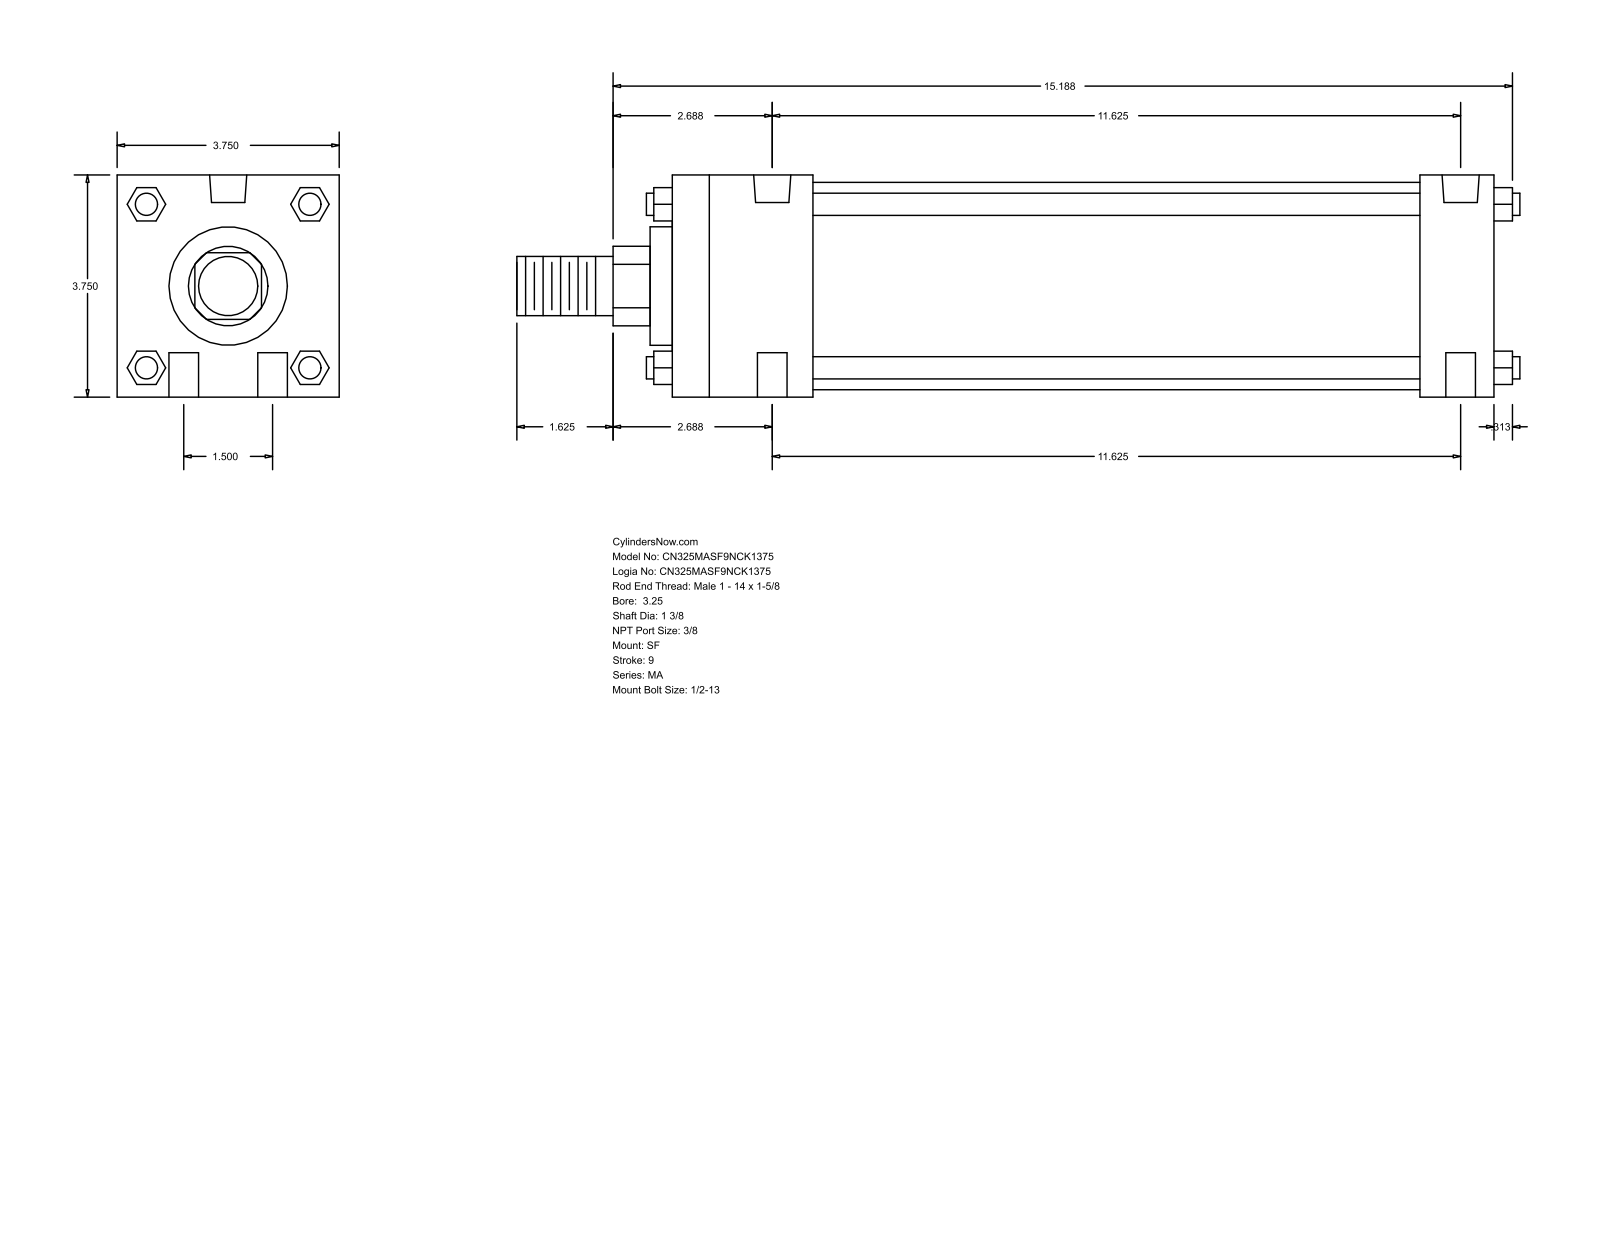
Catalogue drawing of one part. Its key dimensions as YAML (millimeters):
part_name: "MA_SF__0325_1.375"
step_written_by: "GSSL Pune (CONFIG_CONTROL_DESIGN)"
units: millimeters
bodies: {solids: 0, faces: 124, planar: 94, cylindrical: 30, other: 0}
overall_size: [430.21, 95.25, 95.25]
round_holes:
  - {diameter: 12.7, count: 4}
  - {diameter: 11.11, count: 2}
  - {diameter: 15.93, count: 2}
round_bosses_or_shafts:
  - {diameter: 9.53, count: 4}
  - {diameter: 88.9, count: 1}
  - {diameter: 50.8, count: 1}
  - {diameter: 34.92, count: 1}
  - {diameter: 25.4, count: 1}
partial_cylinders:
  - {radius: 17.06, count: 1}
face_to_face_distances: [95.24, 352.42, 320.67, 31.75, 60.32, 260.35, 292.1, 9.52, 69.84, 330.19]
hole_center_spacings: [19.05, 295.89, 295.28, 38.1, 297.73, 285.74]
